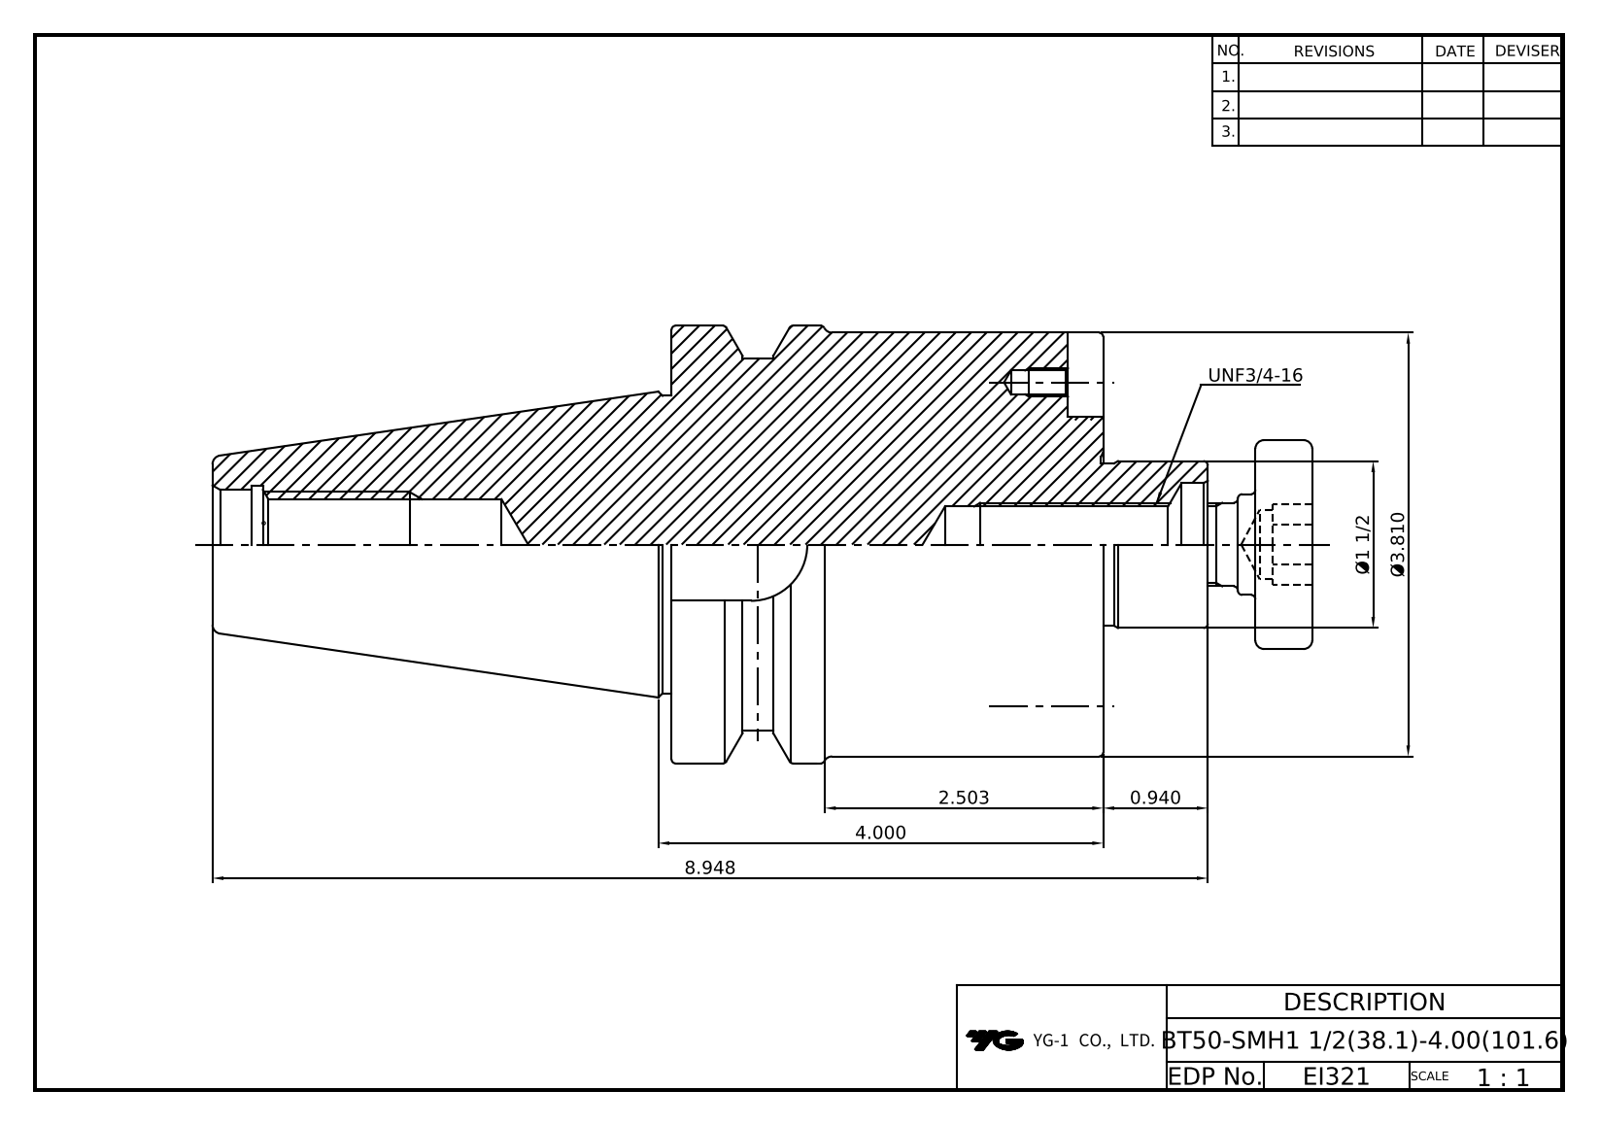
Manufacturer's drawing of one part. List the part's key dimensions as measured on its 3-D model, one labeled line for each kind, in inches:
Part name (STEP PRODUCT): LO-BT50-SMA38.1-101.6; DRIVE KEY-15.875x15.875x18.5; HEX'' WRENCH BOLT-UNC1_4-20x5_8L; COLLAR BOLT-UNF3_4-16x47L
STEP written by: Autodesk Inventor 2025 (AP242_MANAGED_MODEL_BASED_3D_ENGINEERING_MIM_LF)
Units: inches
Bodies: 6 solids, 132 faces (68 planar, 33 cylindrical, 31 other)
Overall size (bounding box): 10.05 × 3.937 × 3.937
Volume: 58.26 in³ · Surface area: 148.3 in²
Round holes (diameter × count): ⌀0.196 ×2, ⌀0.26 ×2, ⌀0.406 ×2, ⌀0.625 ×1, ⌀0.682 ×1, ⌀0.817 ×1, ⌀0.925 ×1, ⌀0.984 ×1, ⌀1.008 ×1
Round bosses / shafts (diameter × count): ⌀0.375 ×2, ⌀0.25 ×2, ⌀3.937 ×1, ⌀3.81 ×1, ⌀3.331 ×1, ⌀2.728 ×1, ⌀1.878 ×1, ⌀1.5 ×1
Partial cylindrical surfaces — rounded edges, fillets, slot ends (radius × count): R0.312 ×2, R0.506 ×1
Main face-to-face distances: 3.882, 5.924, 2.042, 0.512, 5.412, 1.53, 3.564, 0.318, 1.848, 2.36
Hole centre spacings: 1.457, 2.915
